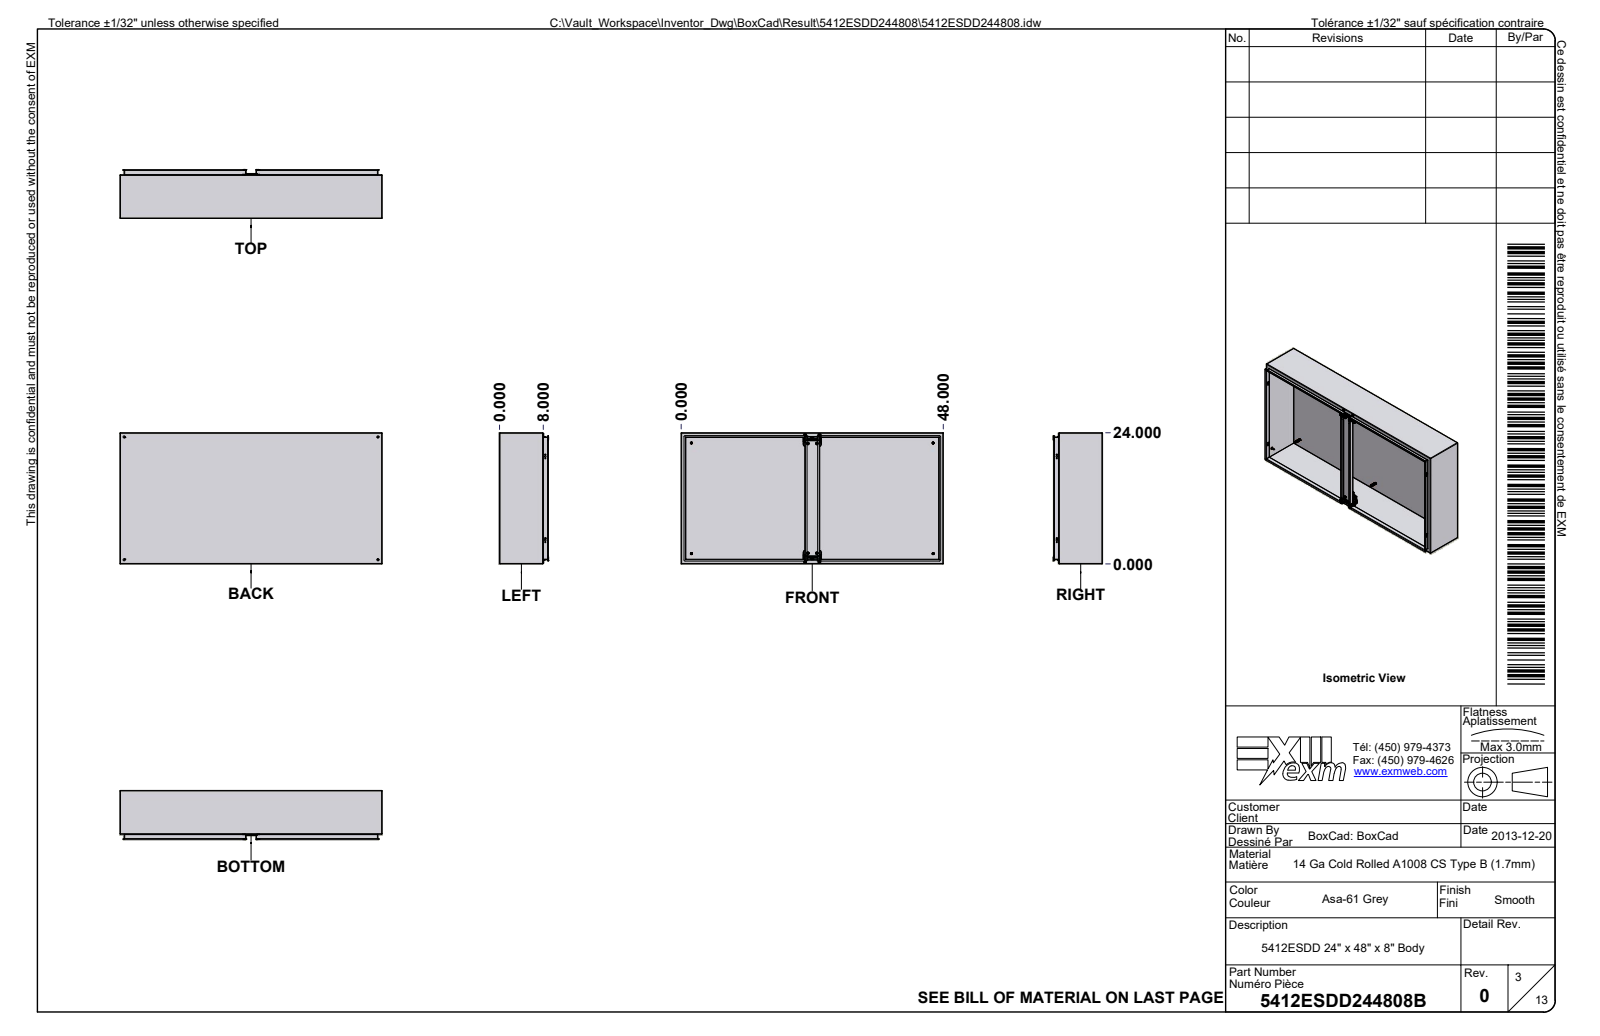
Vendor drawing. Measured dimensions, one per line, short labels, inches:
name: 5412ESDD244808; 5412ESDD244808B; 5412ESDD244808B-P; 5412ESDD244808CP-P (+8 more)
written by: Autodesk Inventor 2024 (AUTOMOTIVE_DESIGN)
unit: in
bodies: 155 solids, 25420 faces (8062 planar, 6916 cylindrical, 10442 other)
size: 48.036 × 24 × 9.28
volume: 393.6 in³; area: 10 802 in²
holes: 80× ⌀0.165, 15× ⌀0.03, 14× ⌀0.201, 14× ⌀0.315, 12× ⌀0.043, 12× ⌀0.311, 8× ⌀0.197, 8× ⌀0.268, 8× ⌀0.287, 6× ⌀0.236, 6× ⌀0.24, 6× ⌀0.27
bosses: 80× ⌀0.237, 25× ⌀0.232, 15× ⌀0.03, 12× ⌀0.472, 12× ⌀0.039, 8× ⌀0.374, 8× ⌀0.177, 6× ⌀0.717
rounds: 888× R0.02, 499× R0.039, 340× R0.008, 266× R0.01, 84× R0.012, 68× R0.079, 64× R0.118, 60× R0.03
face distances: 0.068, 8.983, 9.052, 0.053, 9.104, 9.036, 0.942, 0.874, 8.109, 8.162
hole spacings: 2.625, 21.941, 22.125, 23.486, 24.565, 15.303, 0.35, 0.499
